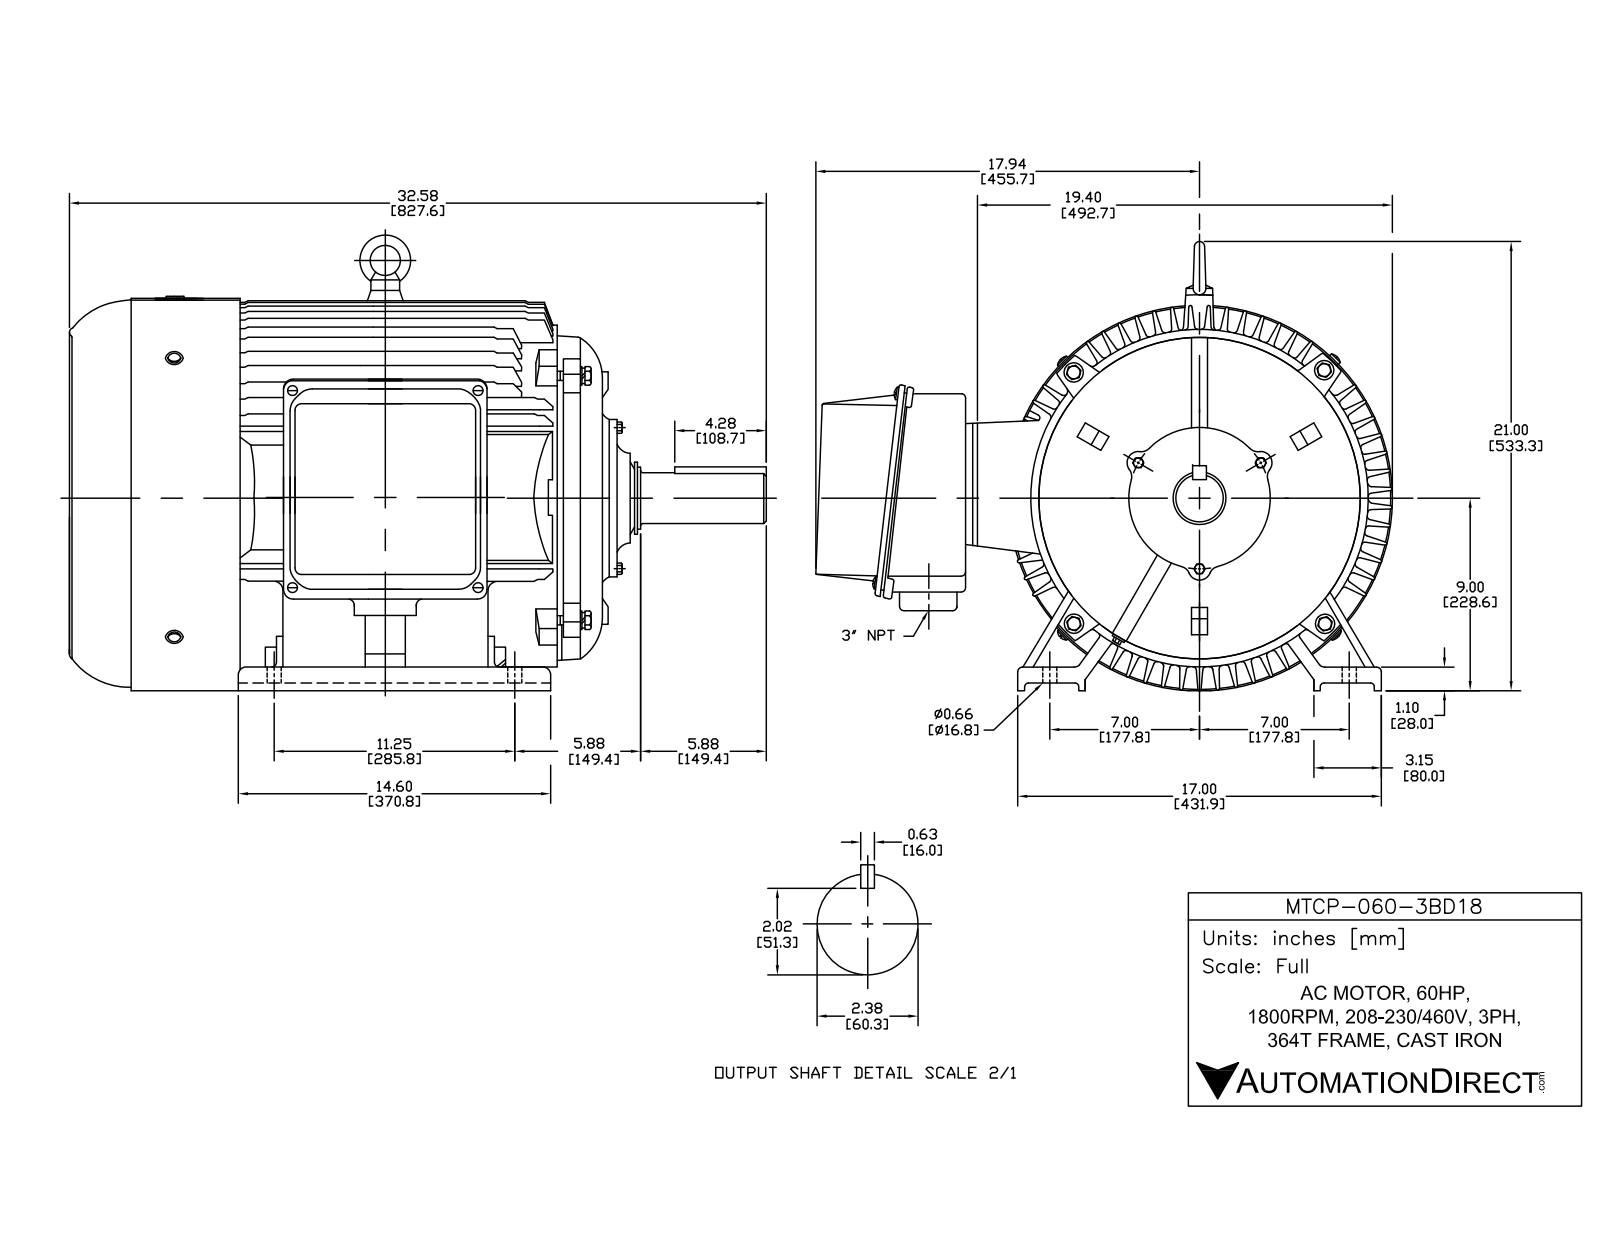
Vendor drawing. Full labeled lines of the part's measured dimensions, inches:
Part name (STEP PRODUCT): MTCP364T; hex head bolts-full thread grade c gb_GB_FASTENER_BOLT_HHBFTC M10X50-N; spring lock washers--normal type gb_GB_FASTENER_WASHER_SW 6; hex head bolts-full thread grade c gb_GB_FASTENER_BOLT_HHBFTC M6X12-N (+8 more)
STEP written by: SolidWorks 2017 (AUTOMOTIVE_DESIGN)
Units: inches
Bodies: 64 solids, 4142 faces (1082 planar, 1553 cylindrical, 1507 other)
Overall size (bounding box): 33.169 × 26.456 × 21.37
Volume: 1 157 in³ · Surface area: 7 409 in²
Round holes (diameter × count): ⌀0.394 ×19, ⌀0.268 ×10, ⌀0.472 ×5, ⌀0.197 ×4, ⌀0.236 ×4, ⌀0.252 ×4, ⌀0.263 ×4, ⌀0.402 ×4, ⌀0.508 ×4, ⌀0.512 ×4, ⌀0.591 ×4, ⌀0.669 ×4
Round bosses / shafts (diameter × count): ⌀0.472 ×8, ⌀0.315 ×8, ⌀0.945 ×4, ⌀0.752 ×4, ⌀0.394 ×4, ⌀0.389 ×4, ⌀0.236 ×4, ⌀18.937 ×1
Partial cylindrical surfaces — rounded edges, fillets, slot ends (radius × count): R0.039 ×224, R0.197 ×152, R0.02 ×83, R0.079 ×65, R0.059 ×40, R0.236 ×34, R0.472 ×20, R0.177 ×18
Main face-to-face distances: 0.236, 0.059, 0.315, 0.551, 0.197, 25.571, 25.512, 8.898, 1.123, 17.835
Hole centre spacings: 5.118, 2.953, 3.248, 5.372, 3.111, 8.976, 0.295, 3.604
